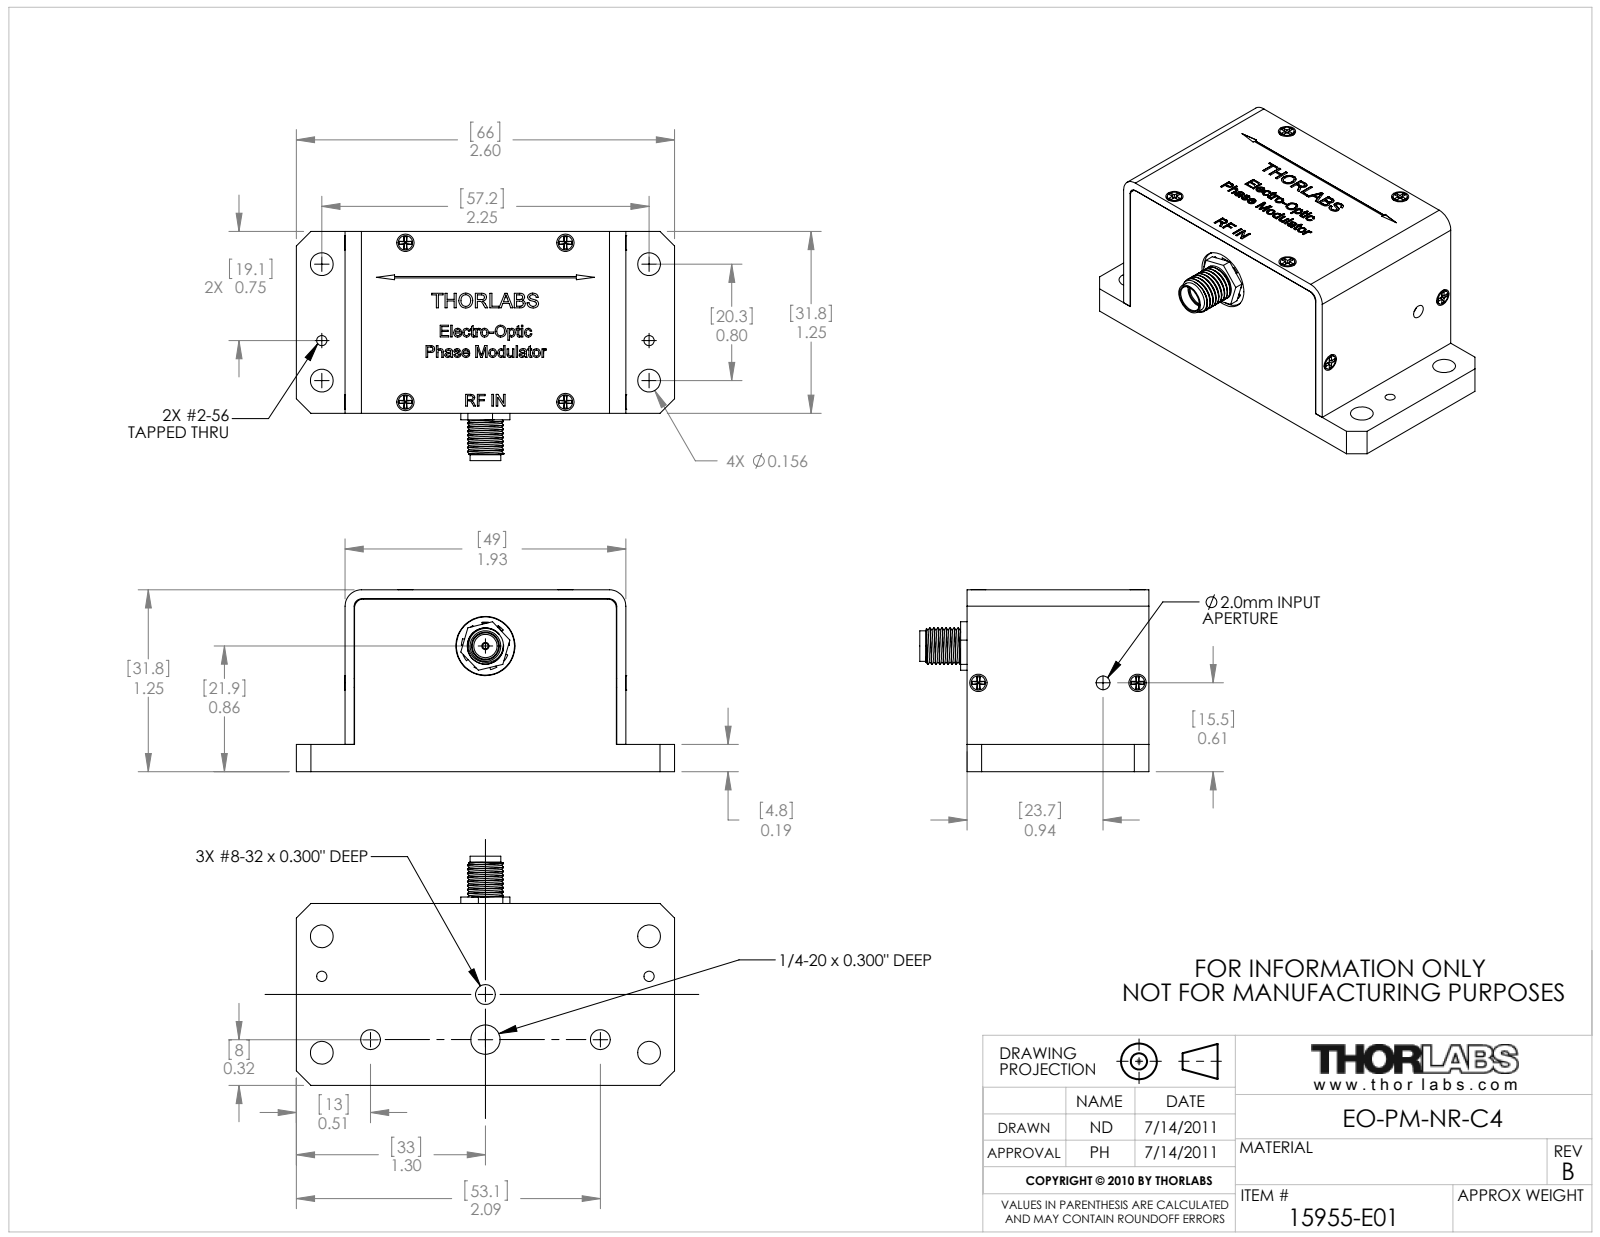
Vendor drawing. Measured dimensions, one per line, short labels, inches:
name: 15955-E01
written by: SolidWorks 2011 (AUTOMOTIVE_DESIGN)
unit: in
bodies: 13 solids, 997 faces (529 planar, 171 cylindrical, 297 other)
size: 2.6 × 1.575 × 1.252
volume: 1.741 in³; area: 28.94 in²
holes: 8× ⌀0.07, 6× ⌀0.047, 4× ⌀0.156, 3× ⌀0.136, 1× ⌀0.037, 1× ⌀0.05, 1× ⌀0.094, 1× ⌀0.16, 1× ⌀0.165, 1× ⌀0.181, 1× ⌀0.201, 1× ⌀0.25
bosses: 6× ⌀0.099, 6× ⌀0.06, 1× ⌀0.4, 1× ⌀0.315, 1× ⌀0.248, 1× ⌀0.21, 1× ⌀0.05
rounds: 2× R0.05, 2× R0.063, 2× R0.113, 2× R0.125, 2× R0.128, 1× R0.137, 1× R0.165
face distances: 1.25, 0.125, 1.125, 1.188, 0.063, 1.867, 1, 0.062, 0.35, 0.838
hole spacings: 0.594, 0.776, 1.108, 1.194, 1.681, 1.924, 1.094, 2.25
